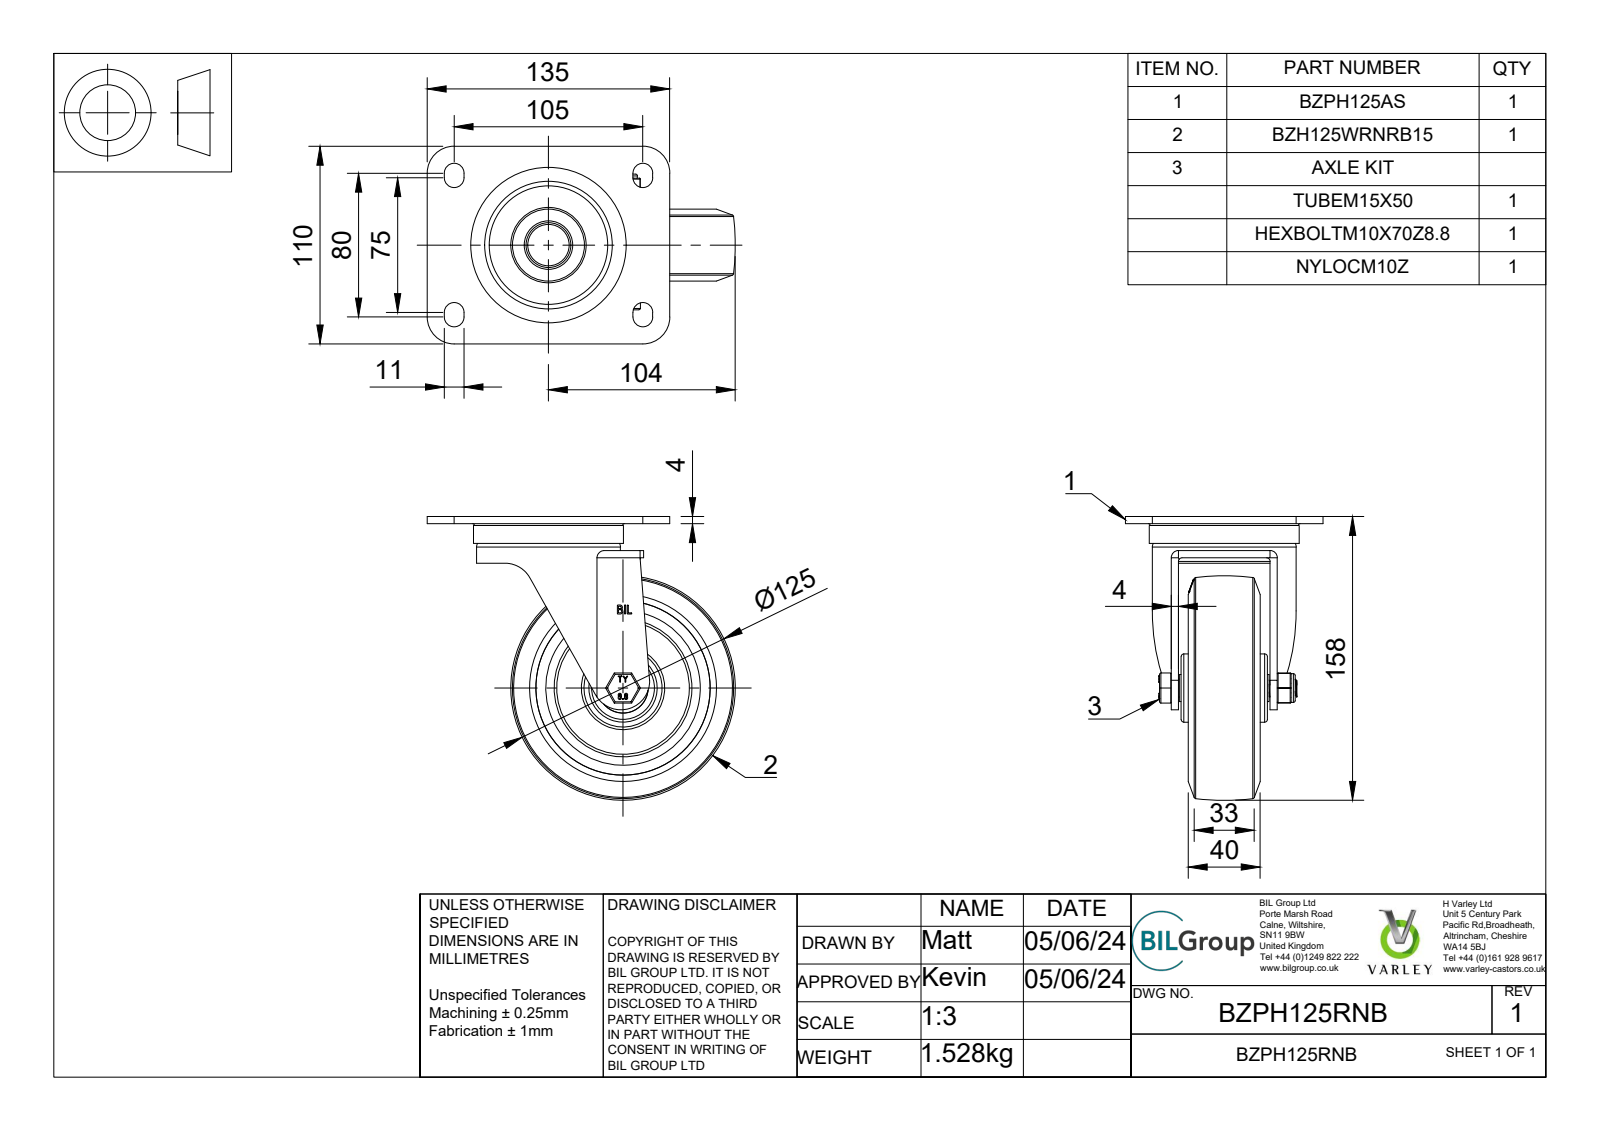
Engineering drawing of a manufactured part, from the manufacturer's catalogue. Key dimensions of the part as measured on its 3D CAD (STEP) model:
Part name (STEP PRODUCT): BZPH125RNB v3; BZPH125AS v1; ZINC PLATED, PRESSED STEEL TOP PLATE; ZINC PLATED, PRESSED STEEL FORKS (+8 more)
STEP written by: Autodesk Translation Framework v13.14.0.145 (AUTOMOTIVE_DESIGN)
Units: millimetres
Bodies: 20 solids, 524 faces (253 planar, 147 cylindrical, 124 other)
Overall size (bounding box): 171.5 × 158 × 110
Volume: 516 459 mm³ · Surface area: 171 496 mm²
Round holes (diameter × count): ⌀10 ×1, ⌀10.2 ×1, ⌀10.5 ×1, ⌀12 ×1, ⌀15 ×1, ⌀17 ×1, ⌀23 ×1, ⌀26 ×1, ⌀28 ×1, ⌀32 ×1, ⌀72 ×1, ⌀82.5 ×1
Round bosses / shafts (diameter × count): ⌀4 ×8, ⌀83.5 ×1, ⌀80 ×1, ⌀51 ×1, ⌀38 ×1, ⌀28 ×1, ⌀27.9 ×1, ⌀25 ×1
Partial cylindrical surfaces — rounded edges, fillets, slot ends (radius × count): R0.5 ×18, R5.5 ×8, R0.75 ×6, R2 ×4, R15 ×4, R4 ×2, R16 ×2, R9.38 ×1
Main face-to-face distances: 4, 13, 9, 15, 25, 49.5, 5.5, 2, 17, 9.5
